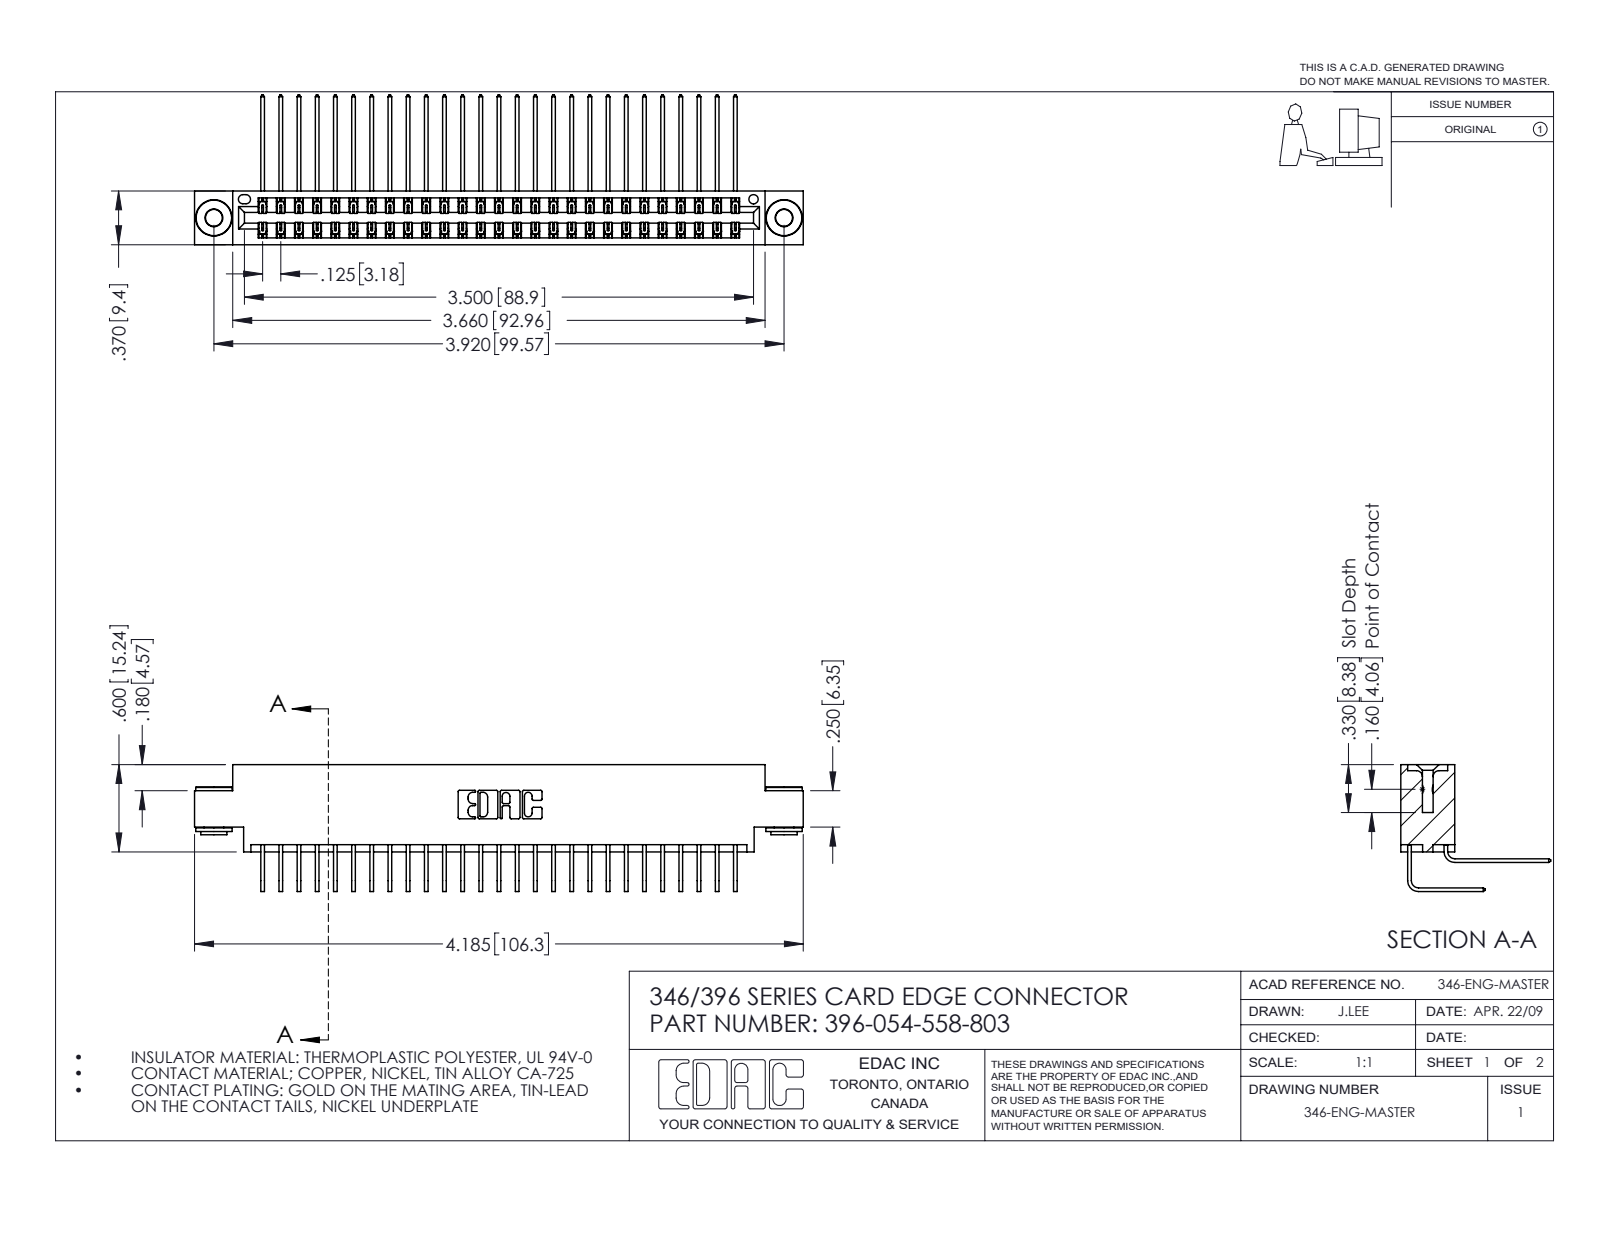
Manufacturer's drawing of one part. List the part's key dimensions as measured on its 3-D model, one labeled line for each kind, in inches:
Part name (STEP PRODUCT): 345-292-001_558 559 Tail - 1; 345-292-001_558 Tail - 2; 345-250-002_345-250-002-102; 346 Part_0.170 Offset - 0.156 Dia-TH (+1 more)
STEP written by: SolidWorks 2016 (CONFIG_CONTROL_DESIGN)
Units: inches
Bodies: 57 solids, 3080 faces (2088 planar, 984 cylindrical, 8 other)
Overall size (bounding box): 4.185 × 1.03 × 0.873
Volume: 0.636 in³ · Surface area: 24.77 in²
Round holes (diameter × count): ⌀0.116 ×2, ⌀0.156 ×2, ⌀0.064 ×1
Round bosses / shafts (diameter × count): ⌀0.25 ×2, ⌀0.18 ×2, ⌀0.136 ×2
Partial cylindrical surfaces — rounded edges, fillets, slot ends (radius × count): R0.006 ×81, R0.01 ×22, R0.007 ×6, R0.031 ×6, R0.026 ×3, R0.014 ×2, R0.022 ×2, R0.024 ×2
Main face-to-face distances: 0.322, 0.048, 0.025, 0.37, 0.25, 0.298, 0.072, 0.275, 0.148, 0.222
Hole centre spacings: 0.246, 3.712, 3.92
